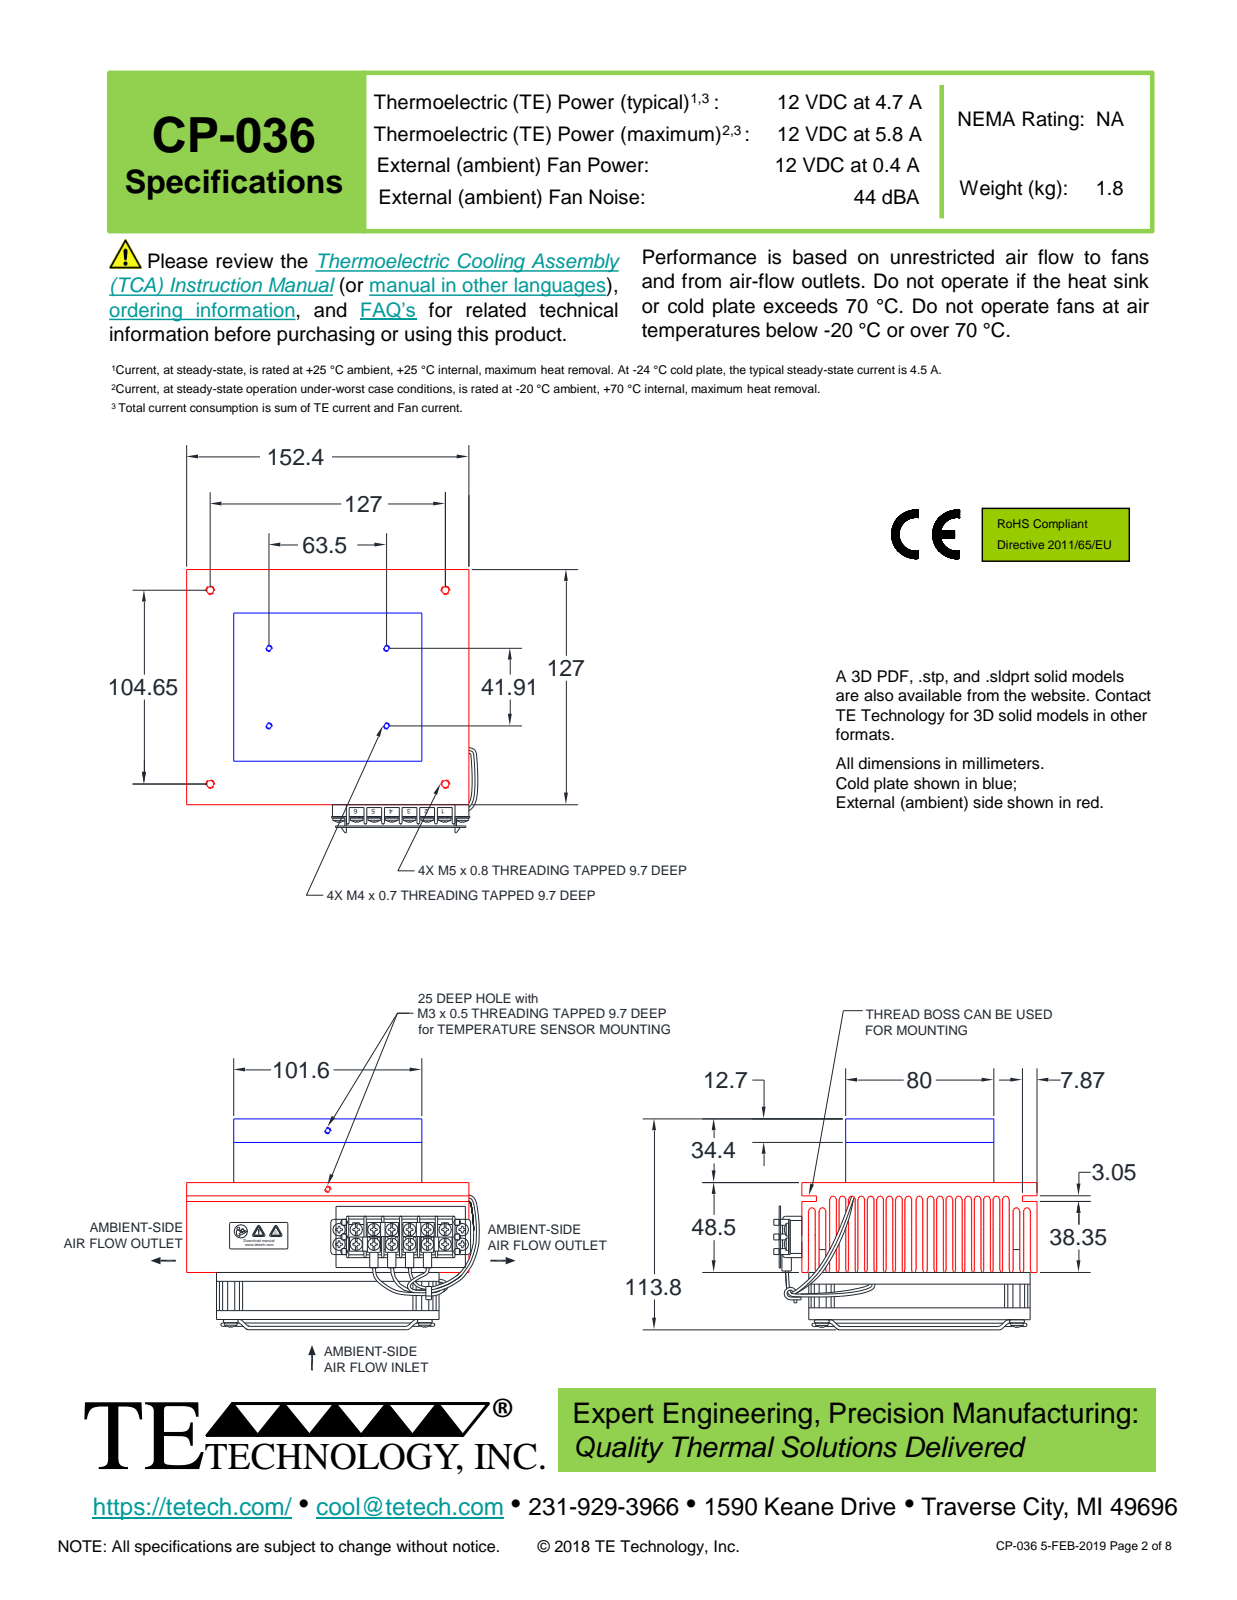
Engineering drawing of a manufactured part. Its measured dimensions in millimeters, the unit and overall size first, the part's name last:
Units: millimetres
Overall size (bounding box): 153.2 × 142.2 × 113.9
Round holes (diameter × count): ⌀2.6 ×18, ⌀1.9 ×4, ⌀3.3 ×4, ⌀3.5 ×4, ⌀3.9 ×4, ⌀4.1 ×4, ⌀4.3 ×4, ⌀4.3 ×4, ⌀4.7 ×4, ⌀3 ×3, ⌀2.5 ×2, ⌀4.2 ×2
Round bosses / shafts (diameter × count): ⌀3.5 ×18, ⌀6.9 ×16, ⌀1.8 ×13, ⌀1.4 ×10, ⌀1.8 ×9, ⌀8.2 ×4, ⌀7.5 ×4, ⌀4.9 ×4
Partial cylindrical surfaces — rounded edges, fillets, slot ends (radius × count): R1 ×59, R0.8 ×54, R0.3 ×52, R1 ×21, R0.8 ×16, R2 ×15, R0.4 ×8, R0.8 ×8
Main face-to-face distances: 5.1, 10.2, 15.2, 52.7, 20.3, 47.6, 57.8, 25.4, 62.9, 42.5
Hole centre spacings: 19.1, 7.9, 20.6, 9.5, 9.5, 12.4, 21.2, 55.2
Volume: 862 100 mm³ · Surface area: 504 000 mm²
Bodies: 125 solids, 3389 faces (1969 planar, 645 cylindrical, 775 other)
Part name (STEP PRODUCT): cover-clip; tb-600 terminal block; terminal-block-cover; terminal block plate (+8 more)
STEP written by: Alibre (AUTOMOTIVE_DESIGN)
